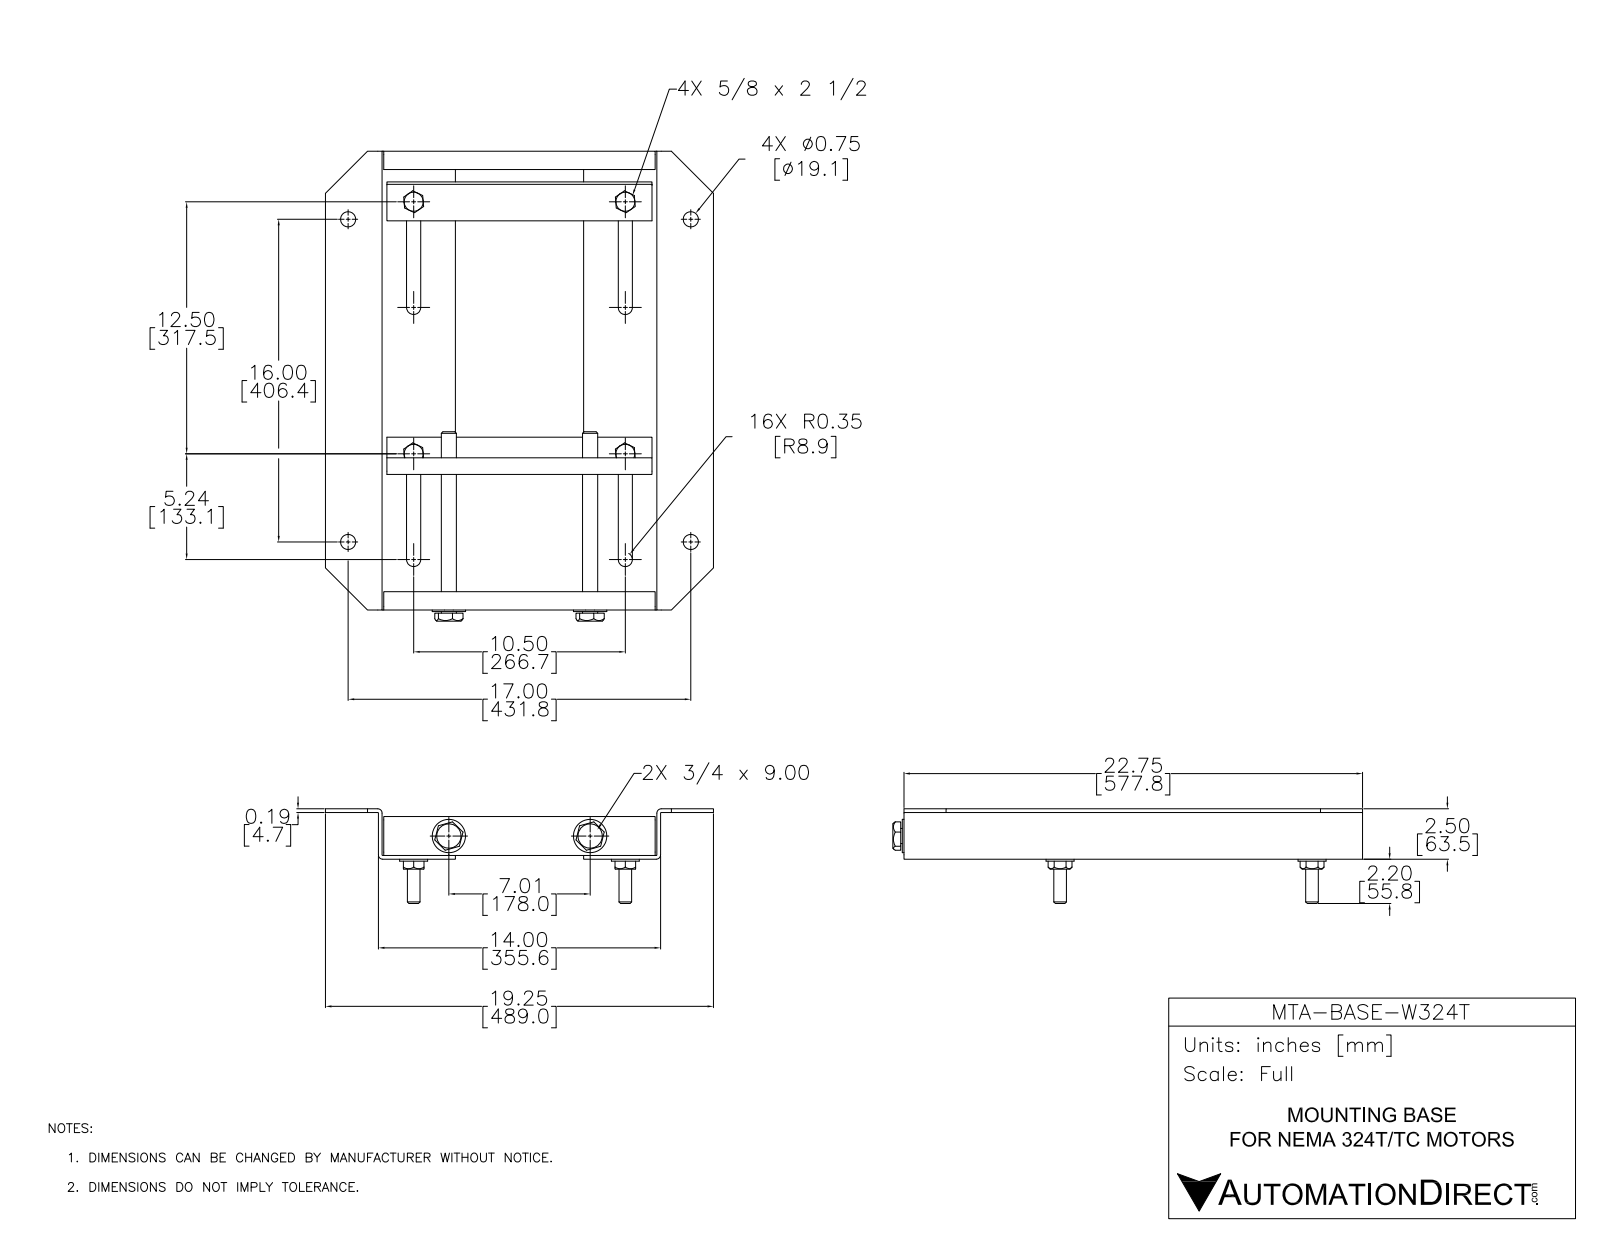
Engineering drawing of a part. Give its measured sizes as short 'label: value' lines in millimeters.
name: MTA-BASE-W324T
written by: SolidWorks 2017 (AUTOMOTIVE_DESIGN)
unit: mm
bodies: 26 solids, 408 faces (224 planar, 108 cylindrical, 76 other)
size: 591.8 × 489 × 119.3
volume: 1 803 000 mm³; area: 841 900 mm²
holes: 6× ⌀19.1, 4× ⌀16, 4× ⌀16.5, 4× ⌀22, 3× ⌀15.9, 2× ⌀20, 1× ⌀15.9
bosses: 4× ⌀35.2, 2× ⌀42, 1× ⌀15.9
rounds: 11× R0.7, 8× R8.9, 6× R4.2, 4× R5.4, 1× R3.7
face distances: 4.7, 58.8, 3.5, 63.5, 54.1, 350.9, 45.5, 3, 355.6, 346.2
hole spacings: 85.5, 138.3, 178, 266.7, 306.7, 317.5, 350, 366.5
